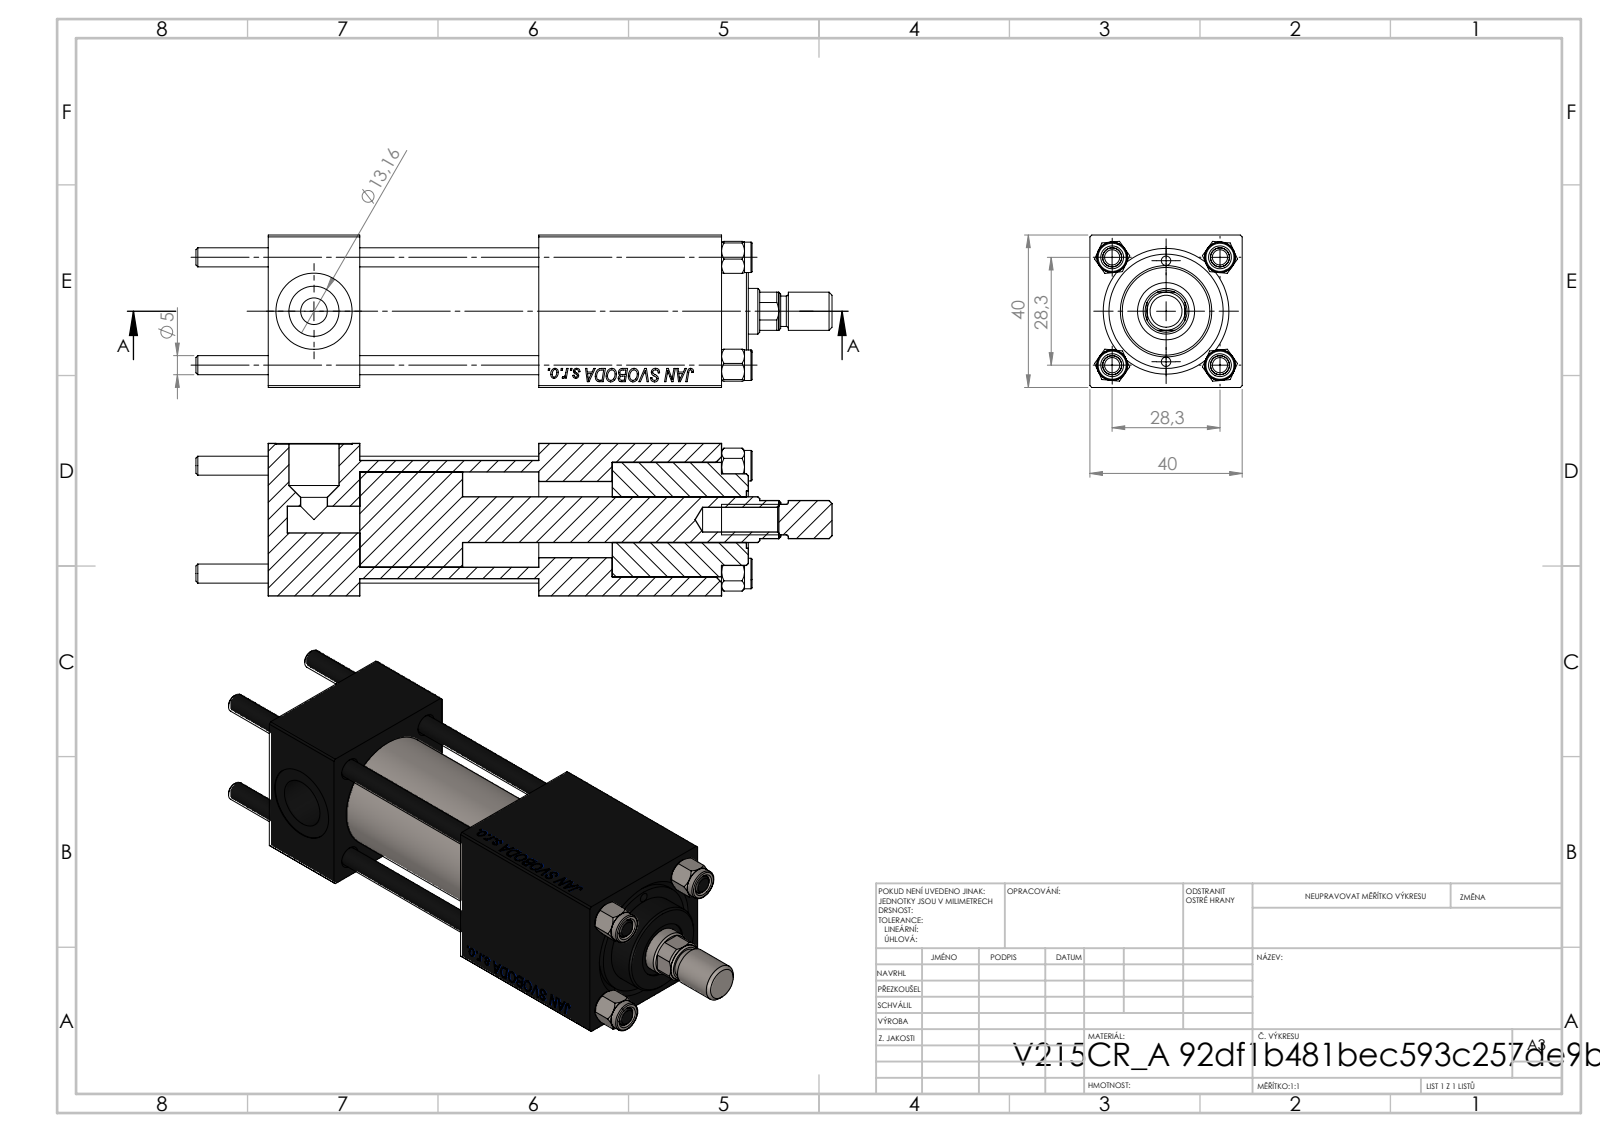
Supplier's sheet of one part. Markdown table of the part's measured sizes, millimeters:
| quantity | value |
| --- | --- |
| part name | ROD_END_AH; NUT_M5; V215CR_BODY_A; V215CR_VCP (+2 more) |
| STEP written by | SolidWorks 2019 (CONFIG_CONTROL_DESIGN) |
| units | millimeters |
| bodies | 12 solids, 1152 faces (523 planar, 87 cylindrical, 542 other) |
| overall size | 167 × 40 × 40 |
| volume | 145 725 mm³ |
| surface area | 59 562 mm² |
| round holes (diameter × count) | 5 × 4, 20 × 3, 2.5 × 2, 7 × 2, 13.16 × 2, 6.5 × 1, 12 × 1, 15 × 1, 25 × 1, 30 × 1 |
| round bosses / shafts (diameter × count) | 8 × 5, 31 × 1, 24 × 1, 10 × 1 |
| partial cylindrical surfaces (radius × count) | 5.5 × 1 |
| main face-to-face distances | 40, 24, 90.3, 66.3, 119, 95, 28.7, 71, 47, 19.3 |
| hole center spacings | 14.18, 20.01, 28.3, 30.84, 13.25, 40.02, 26.5 |
